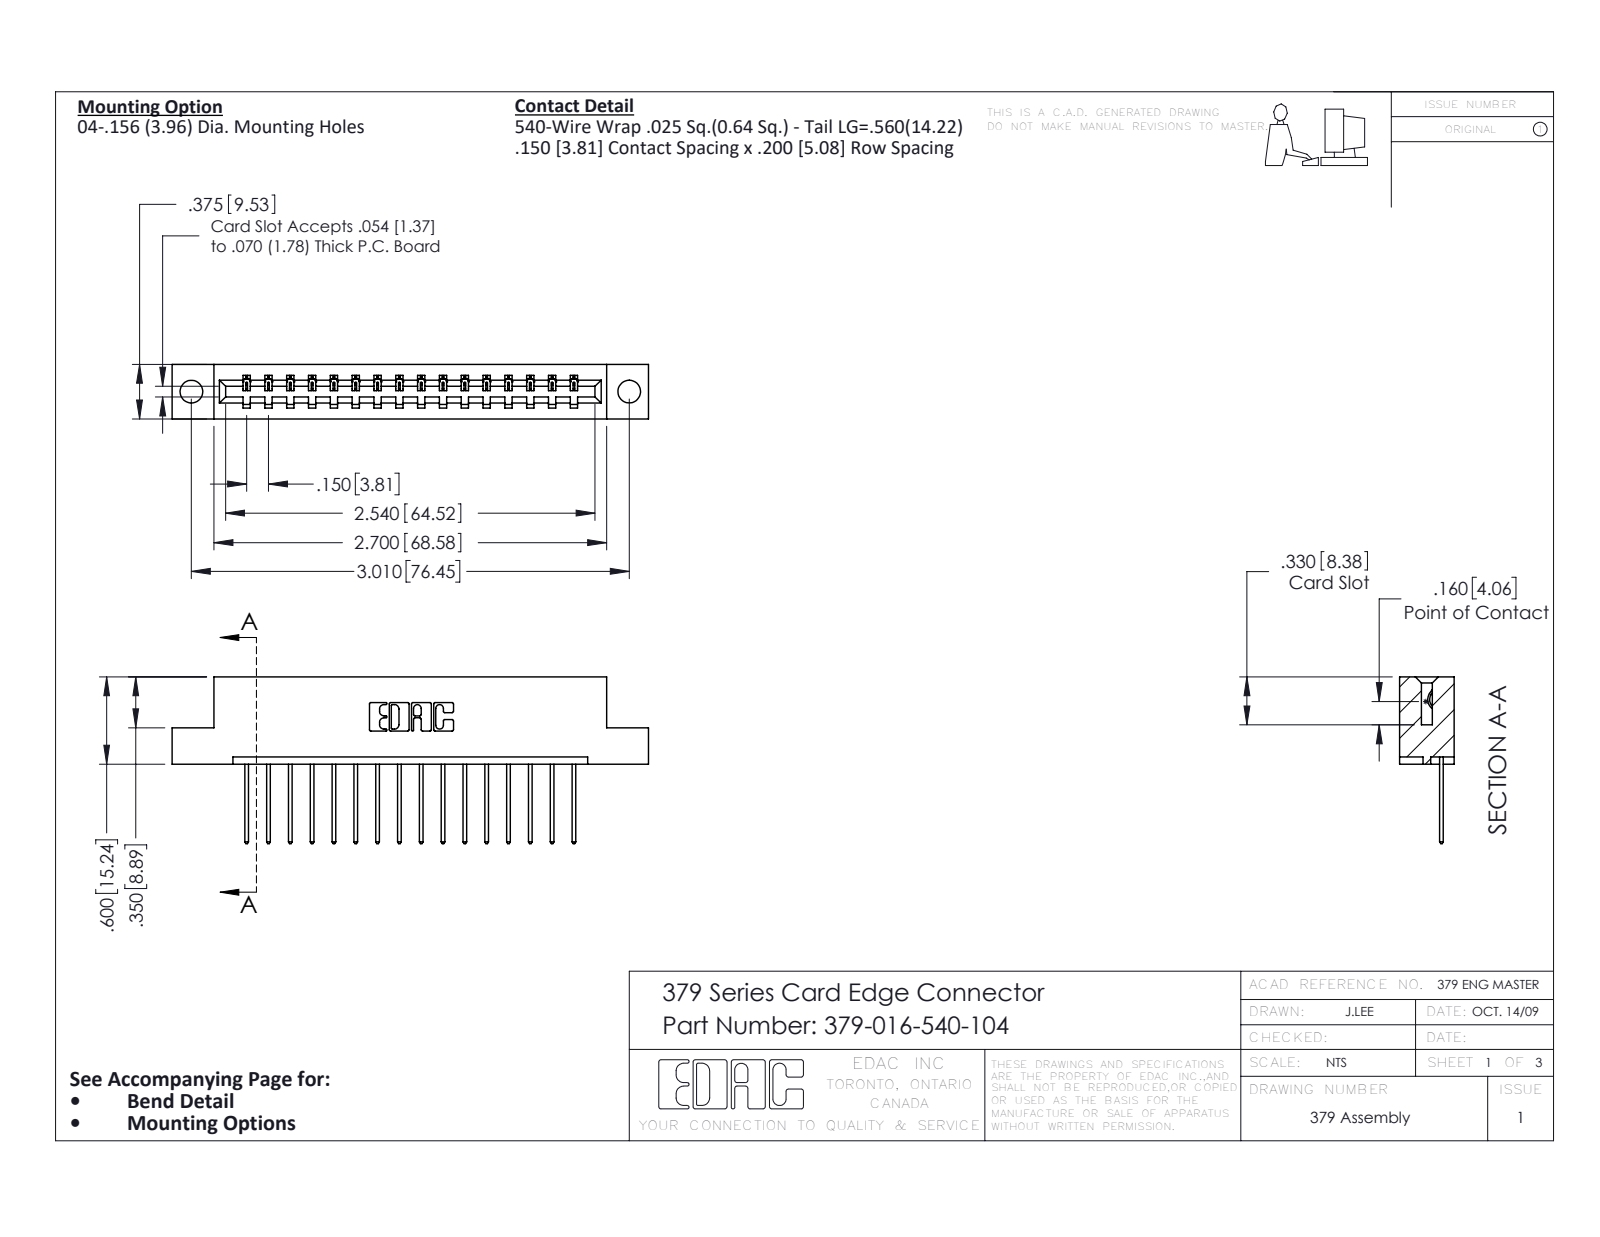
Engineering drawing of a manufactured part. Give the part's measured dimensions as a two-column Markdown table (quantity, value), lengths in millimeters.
| quantity | value |
| --- | --- |
| part name | 379-016-540-104; 379 Part_Flush - .156 Dia - TH; 345-292-001_345-293-140 |
| STEP written by | SolidWorks 2020 (CONFIG_CONTROL_DESIGN) |
| units | millimeters |
| bodies | 17 solids, 1042 faces (742 planar, 300 cylindrical, 0 other) |
| overall size | 83.2 × 29.1 × 9.5 |
| volume | 8 360 mm³ |
| surface area | 8 381 mm² |
| round holes (diameter × count) | 4 × 2 |
| partial cylindrical surfaces (radius × count) | 0.2 × 32, 0.3 × 32, 0.3 × 22, 0.2 × 6, 0.8 × 6, 0.7 × 3, 0.4 × 1, 0.6 × 1 |
| main face-to-face distances | 7.6, 1.9, 9.5, 15.2, 3.8, 5.7, 11.4, 5.1, 19.1, 7 |
| hole center spacings | 76.5 |
